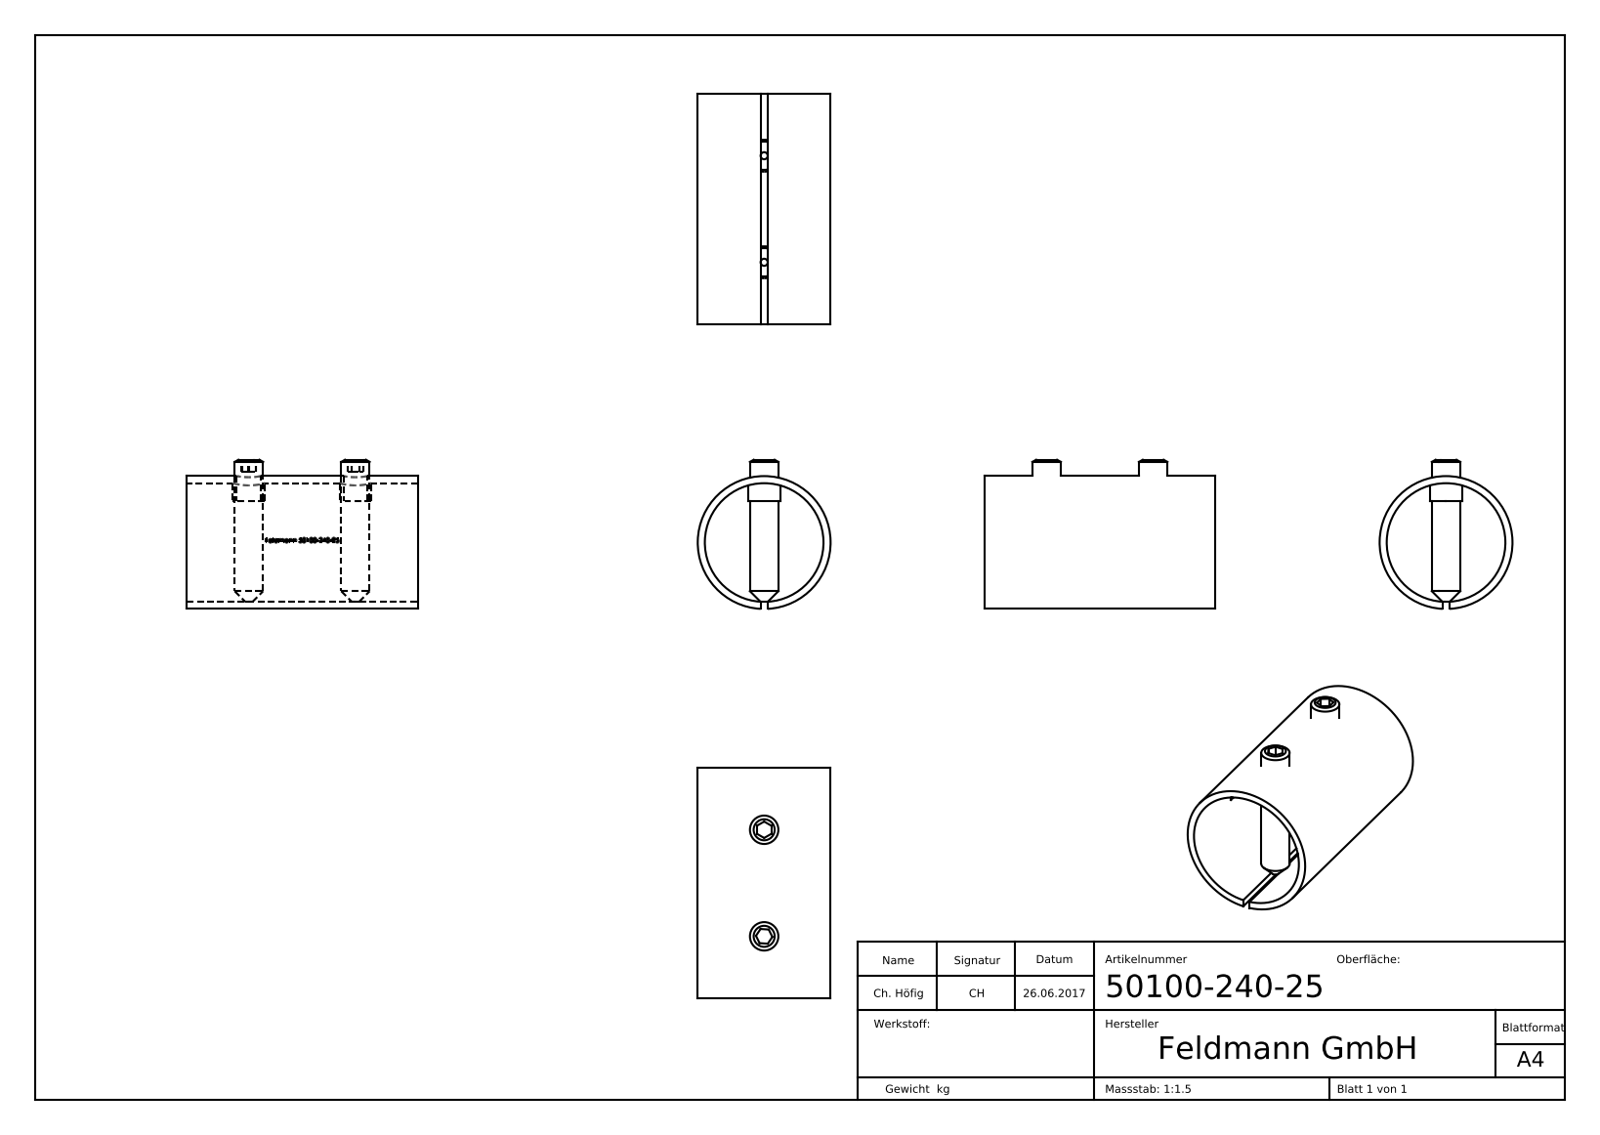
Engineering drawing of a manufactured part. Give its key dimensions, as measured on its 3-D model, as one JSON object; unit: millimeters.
{"part_name": "50100-240-25 DIN 914 M8 x 40_M8 x 40; 50100-240-25; 50100-240-25 Teil1; 50100-240-25 DIN 914 M8 x 40", "step_written_by": "SolidWorks 2018 (CONFIG_CONTROL_DESIGN)", "units": "millimeters", "bodies": {"solids": 3, "faces": 281, "planar": 129, "cylindrical": 36, "other": 116}, "overall_size": [43001.97, 7999.99, 7999.85], "volume_mm3": 18051, "surface_area_mm2": 17490, "round_holes": [[6.8, 2], [33.4, 1]], "round_bosses_or_shafts": [[9, 2], [8, 2], [37.4, 1]], "partial_cylinders_radius": [[16.8, 1]], "face_to_face_distances": [65, 2, 4, 8.1, 11.6, 3.5, 1, 3, 28.4, 36.5], "hole_center_spacings": [30]}
